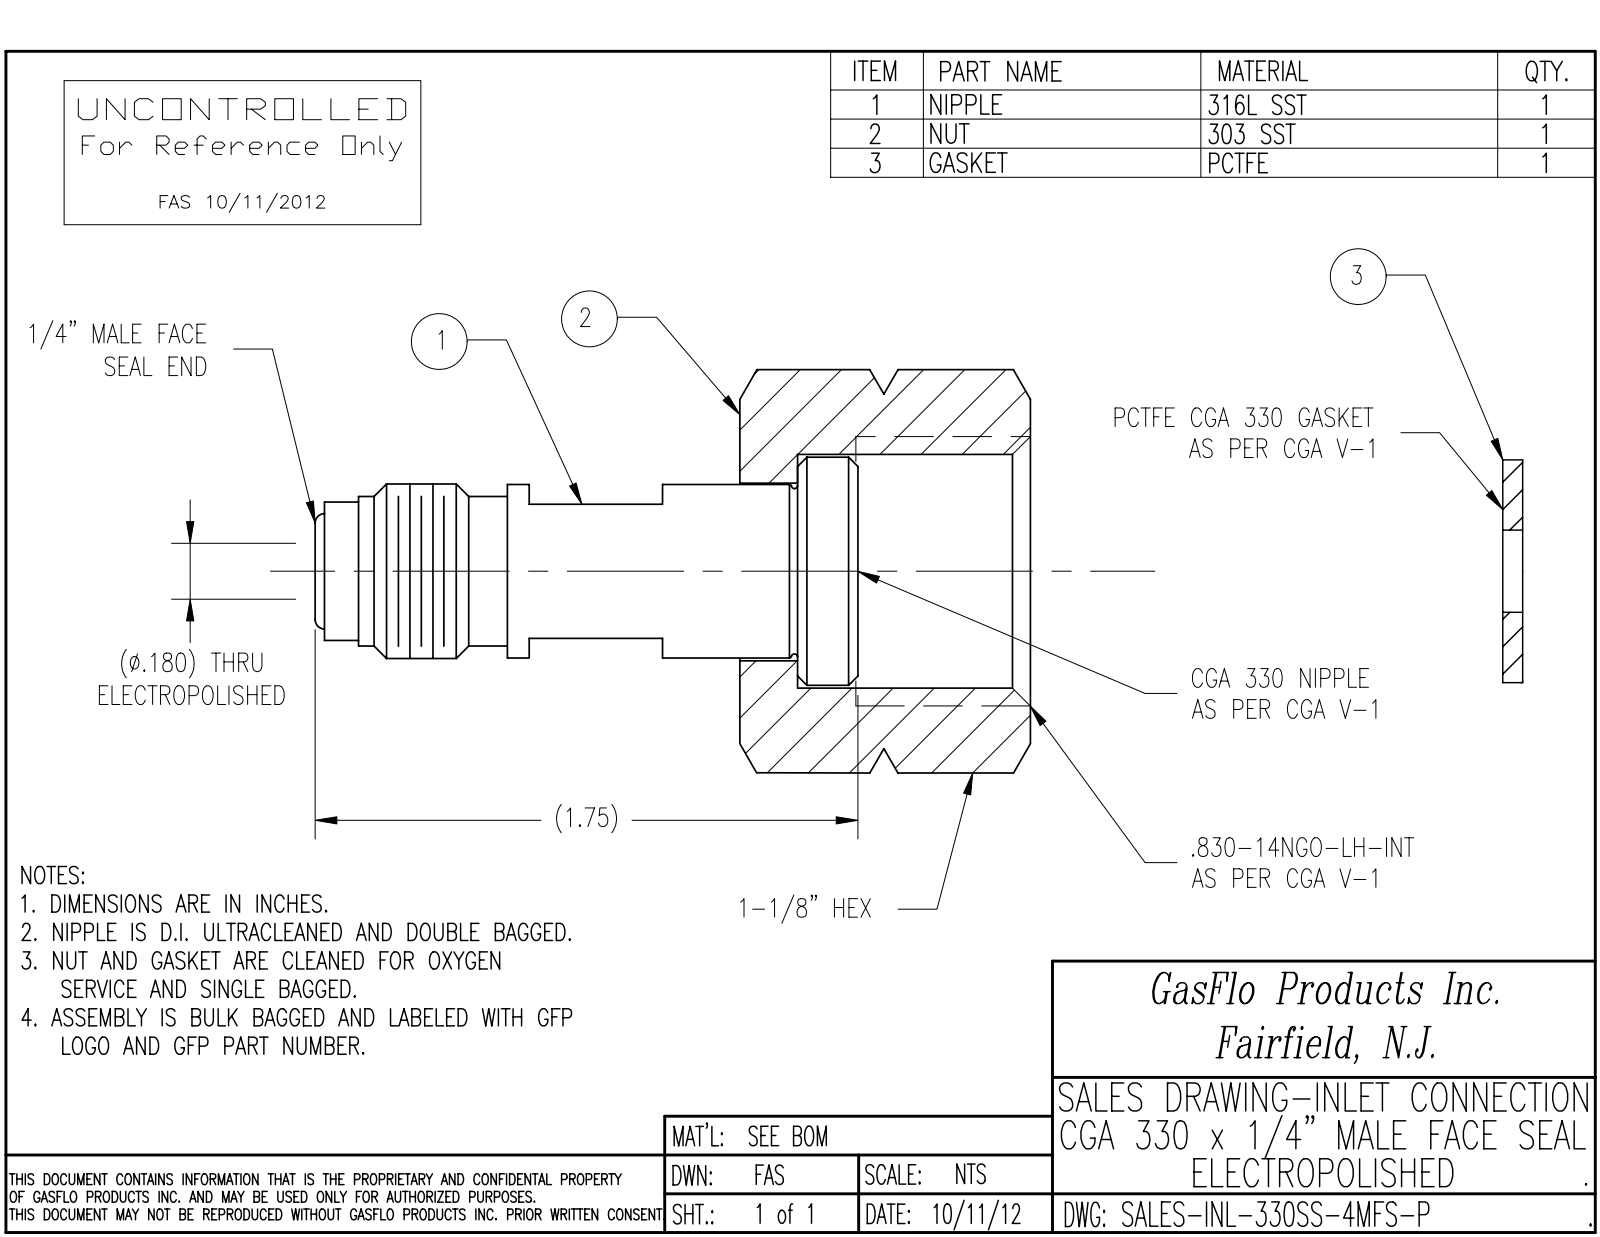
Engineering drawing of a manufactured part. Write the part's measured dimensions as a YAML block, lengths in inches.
part_name: "INL-330SS-4MFS-P"
step_written_by: "SolidWorks 2018 (CONFIG_CONTROL_DESIGN)"
units: inches
bodies: {solids: 3, faces: 210, planar: 40, cylindrical: 44, other: 126}
overall_size: [2.306, 1.299, 1.125]
volume: 1.024
surface_area: 14.27
round_holes:
  - {diameter: 0.179, count: 1}
  - {diameter: 0.236, count: 1}
  - {diameter: 0.25, count: 1}
  - {diameter: 0.57, count: 1}
  - {diameter: 0.757, count: 1}
round_bosses_or_shafts:
  - {diameter: 0.736, count: 1}
  - {diameter: 0.703, count: 1}
  - {diameter: 0.56, count: 1}
  - {diameter: 0.557, count: 1}
  - {diameter: 0.481, count: 1}
  - {diameter: 0.444, count: 1}
  - {diameter: 0.393, count: 1}
face_to_face_distances: [1.125, 0.194, 0.389, 0.944, 0.556, 0.483, 0.094, 0.461, 0.289, 0.75]
